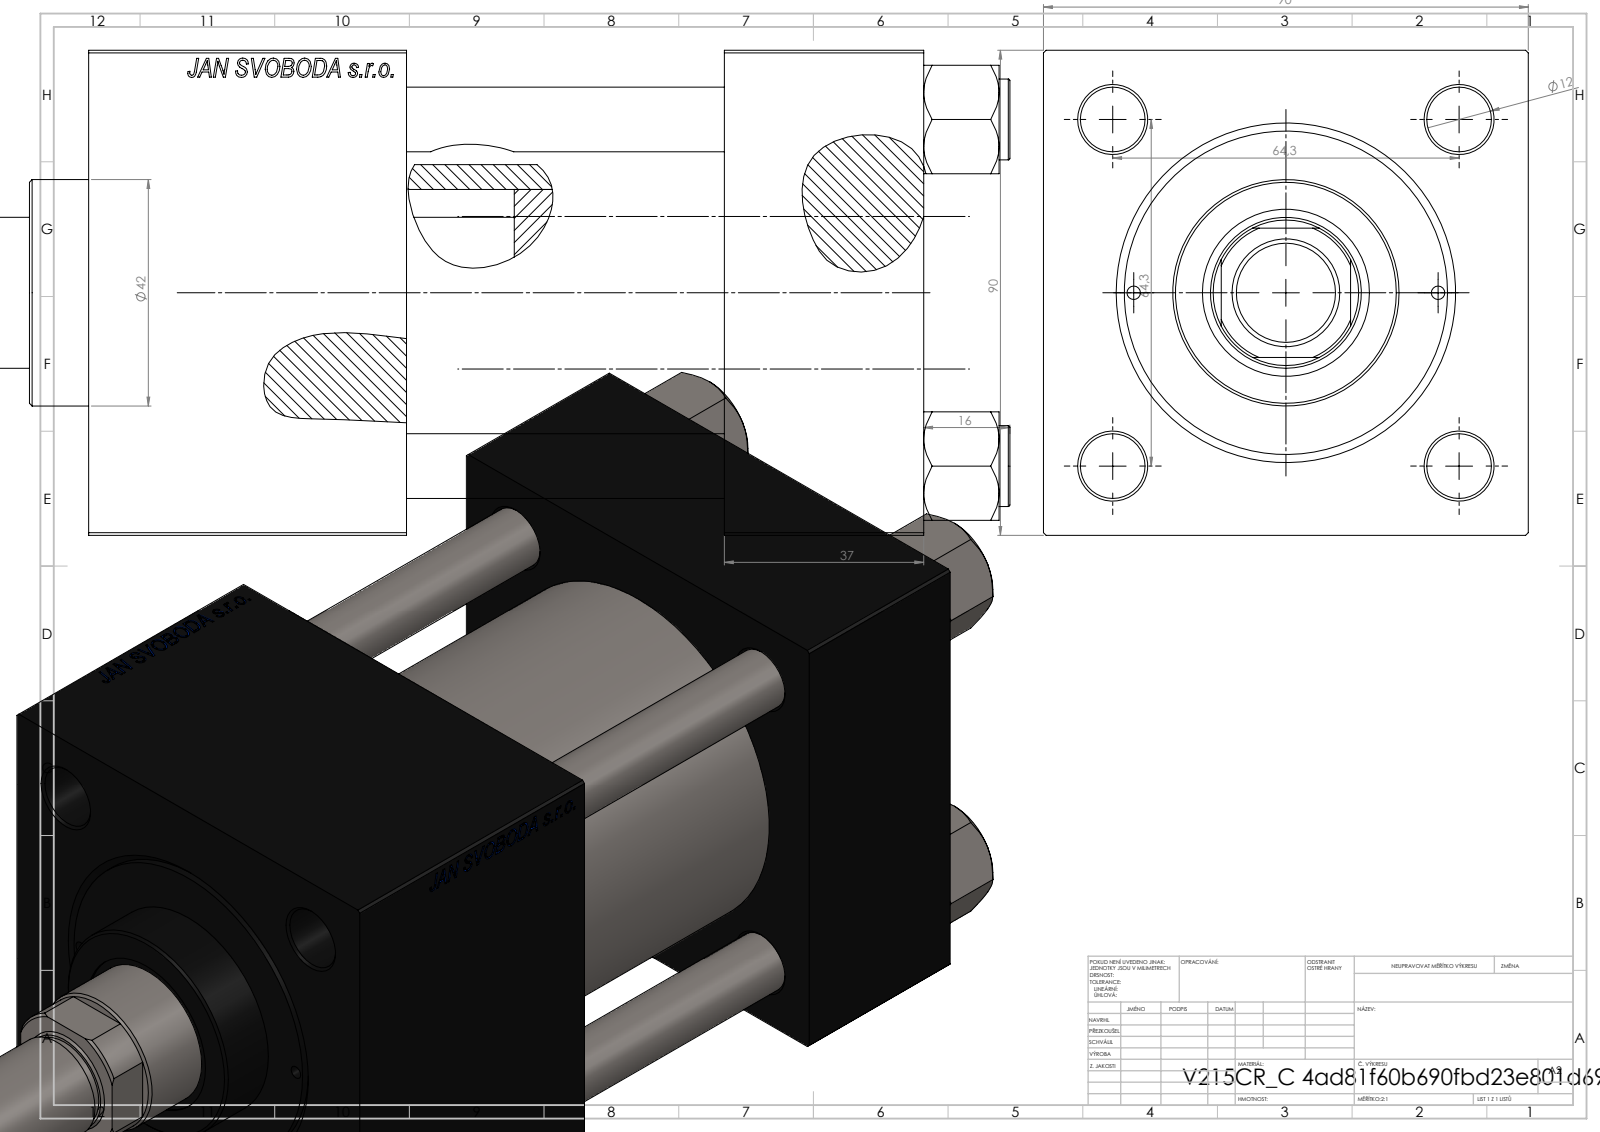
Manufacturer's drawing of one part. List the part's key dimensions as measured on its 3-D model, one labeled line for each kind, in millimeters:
Part name (STEP PRODUCT): ROD_END_AH; V215_VC_A; V215CR_C_Body; V215CR_C_TYCINKA (+2 more)
STEP written by: SolidWorks 2019 (CONFIG_CONTROL_DESIGN)
Units: millimetres
Bodies: 12 solids, 1168 faces (532 planar, 94 cylindrical, 542 other)
Overall size (bounding box): 231 × 90 × 90
Volume: 955 489 mm³ · Surface area: 181 640 mm²
Round holes (diameter × count): ⌀12 ×4, ⌀2.5 ×2, ⌀7 ×2, ⌀20.96 ×2, ⌀30 ×2, ⌀18.5 ×1, ⌀28 ×1, ⌀31 ×1, ⌀50 ×1, ⌀60 ×1, ⌀63 ×1
Round bosses / shafts (diameter × count): ⌀15 ×4, ⌀69 ×1, ⌀42 ×1, ⌀20 ×1, ⌀18 ×1
Partial cylindrical surfaces — rounded edges, fillets, slot ends (radius × count): R13.5 ×1
Main face-to-face distances: 90, 59, 37, 155, 118, 96, 126.3, 89.3, 30.3, 28.7
Hole centre spacings: 32.39, 45.47, 64.3, 68.42, 28.25, 90.93, 56.5, 97.5
